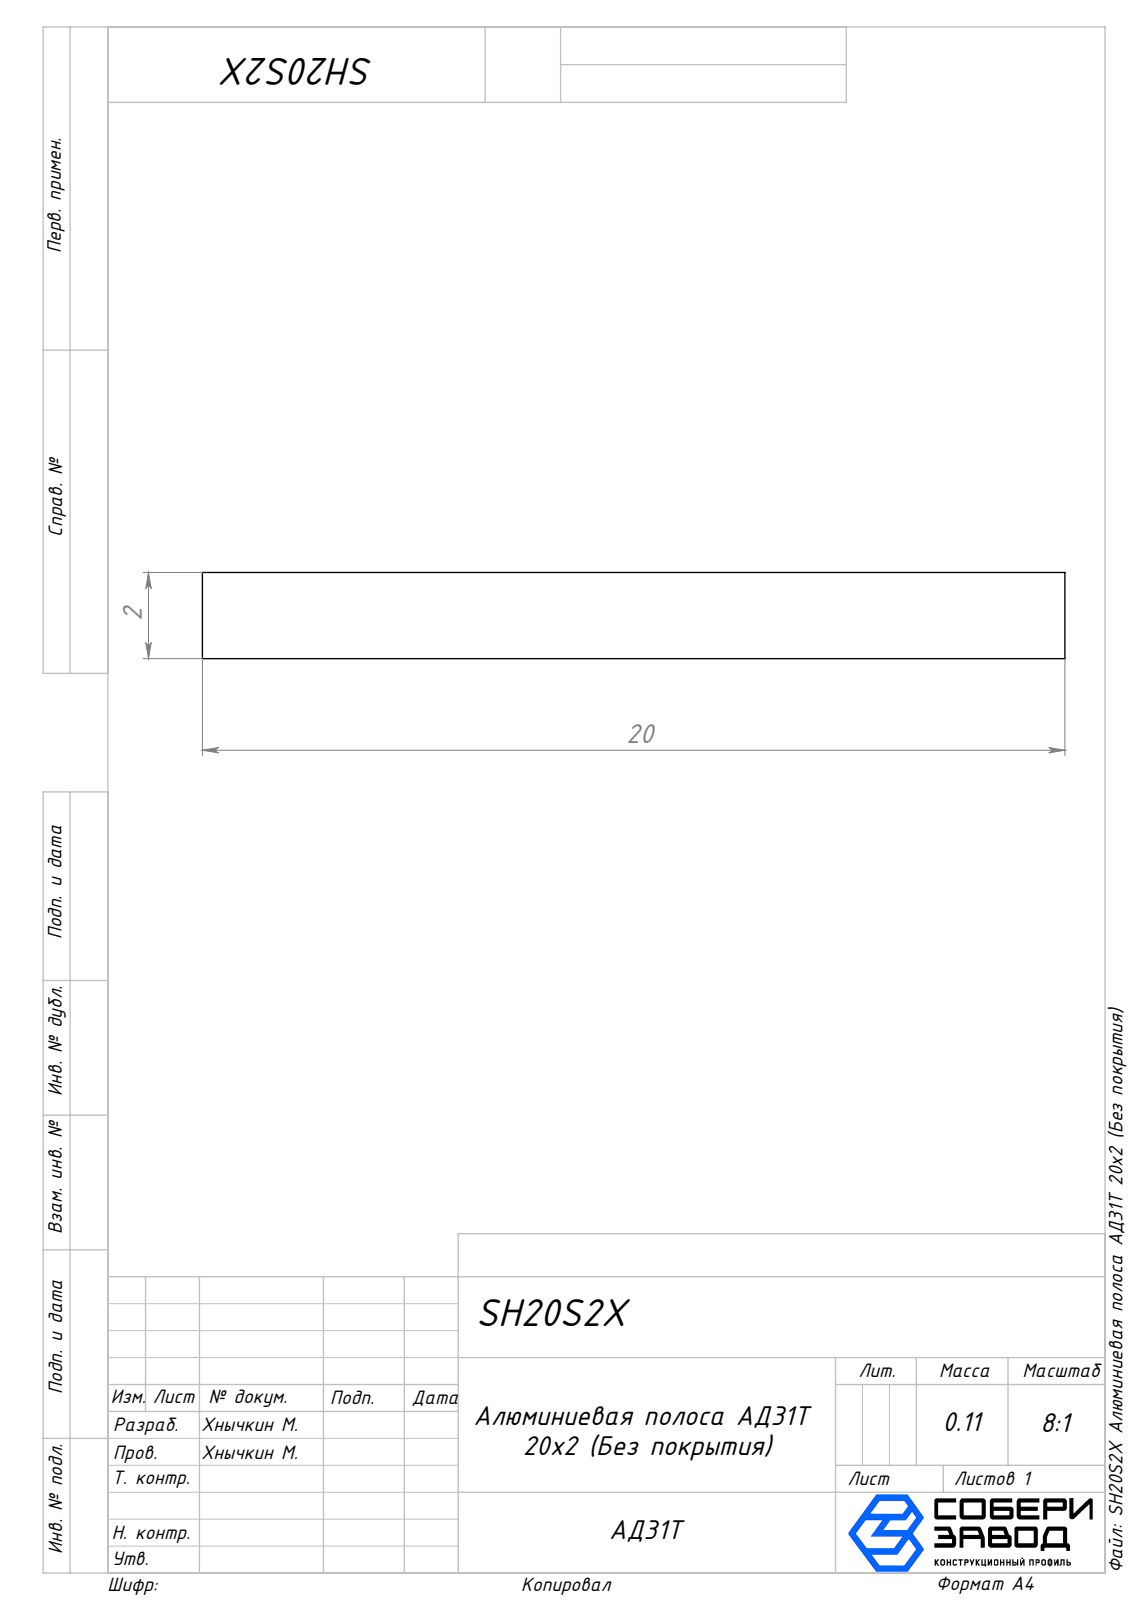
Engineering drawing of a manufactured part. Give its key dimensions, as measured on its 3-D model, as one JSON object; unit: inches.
{"part_name": "SH20S2X Алюминиевая полоса АД31Т 20х2 (Без покрытия)", "step_written_by": "SolidWorks 2025 (AUTOMOTIVE_DESIGN)", "units": "inches", "bodies": {"solids": 1, "faces": 6, "planar": 6, "cylindrical": 0, "other": 0}, "overall_size": [39.37, 0.787, 0.079], "volume_in3": 2.441, "surface_area_in2": 68.32, "face_to_face_distances": [0.079, 0.787, 39.37]}
